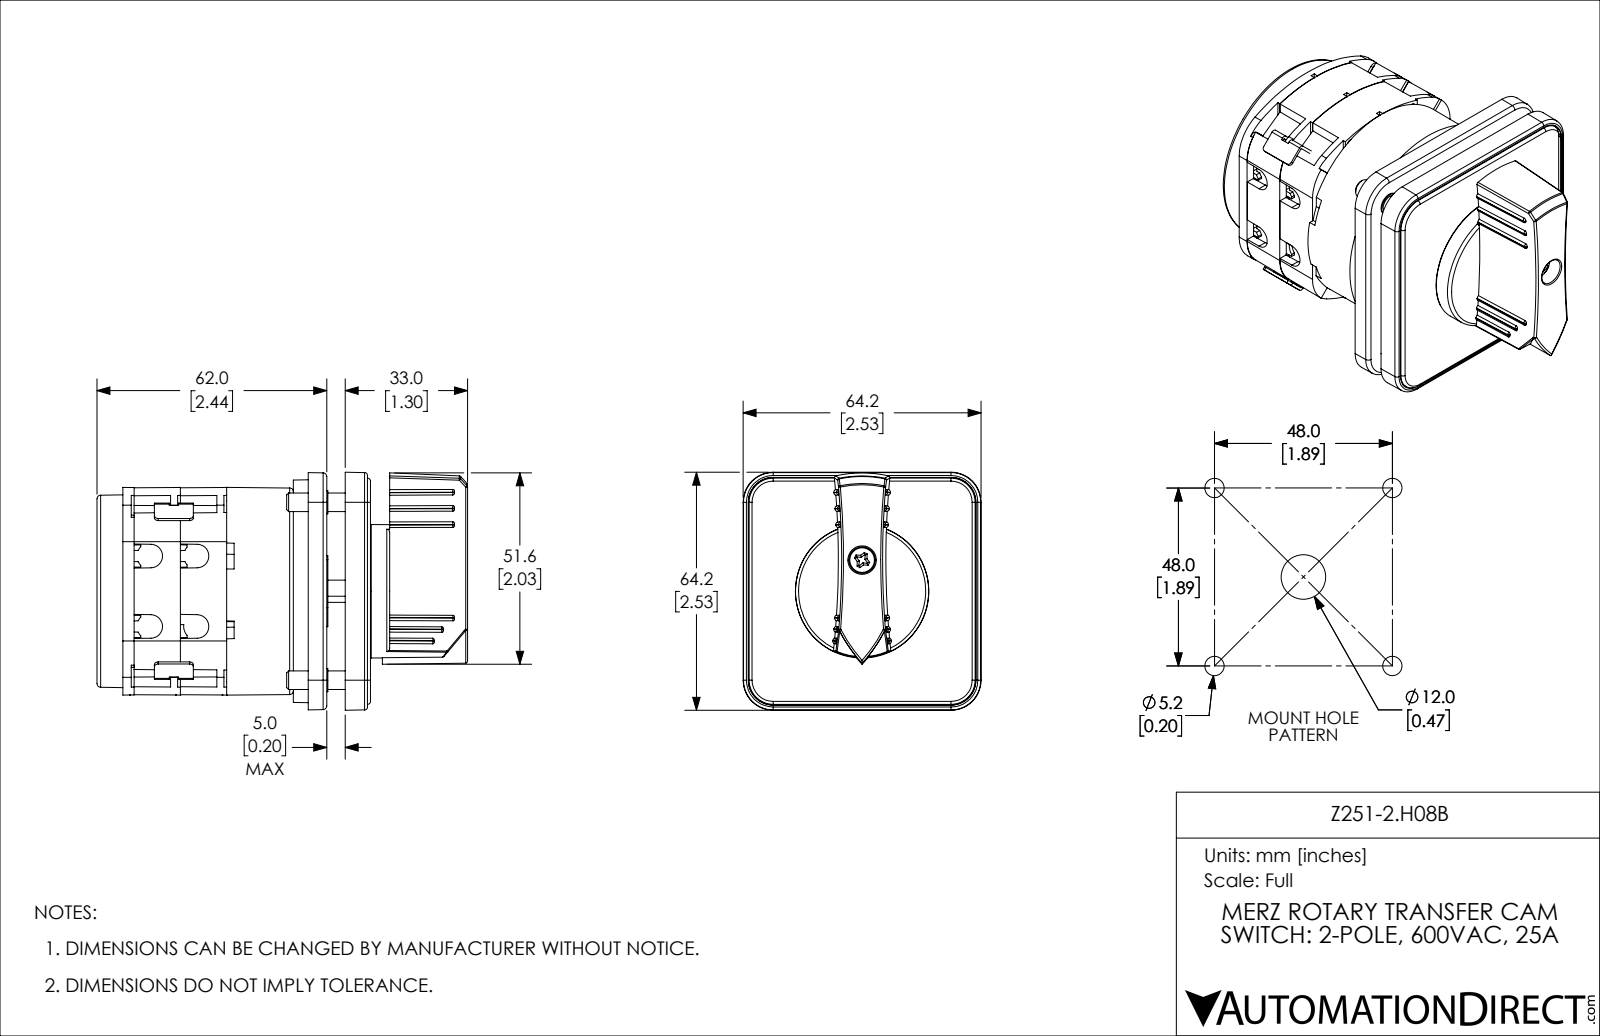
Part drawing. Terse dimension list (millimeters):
name: Z251-2.H08B
written by: SolidWorks 2019 (AUTOMOTIVE_DESIGN)
unit: mm
bodies: 14 solids, 2916 faces (1689 planar, 249 cylindrical, 978 other)
size: 100 × 64.2 × 64.2
volume: 163 600 mm³; area: 89 230 mm²
holes: 6× ⌀8, 4× ⌀0.3, 4× ⌀4, 4× ⌀5, 4× ⌀5.2, 4× ⌀9.5, 1× ⌀13, 1× ⌀23.5
bosses: 4× ⌀9.3, 4× ⌀8.1, 4× ⌀7.3, 4× ⌀5, 1× ⌀7.5, 1× ⌀3.5
rounds: 21× R1, 14× R0.2, 11× R0.8, 6× R0.5, 4× R0.1, 4× R0.2, 4× R0.5, 4× R0.9
face distances: 10, 12.5, 11.8, 1.8, 0.8, 18.2, 19, 5, 9, 20.8
hole spacings: 42.4, 8.5, 9, 9.3, 9.5, 16.4, 16.5, 18.1
